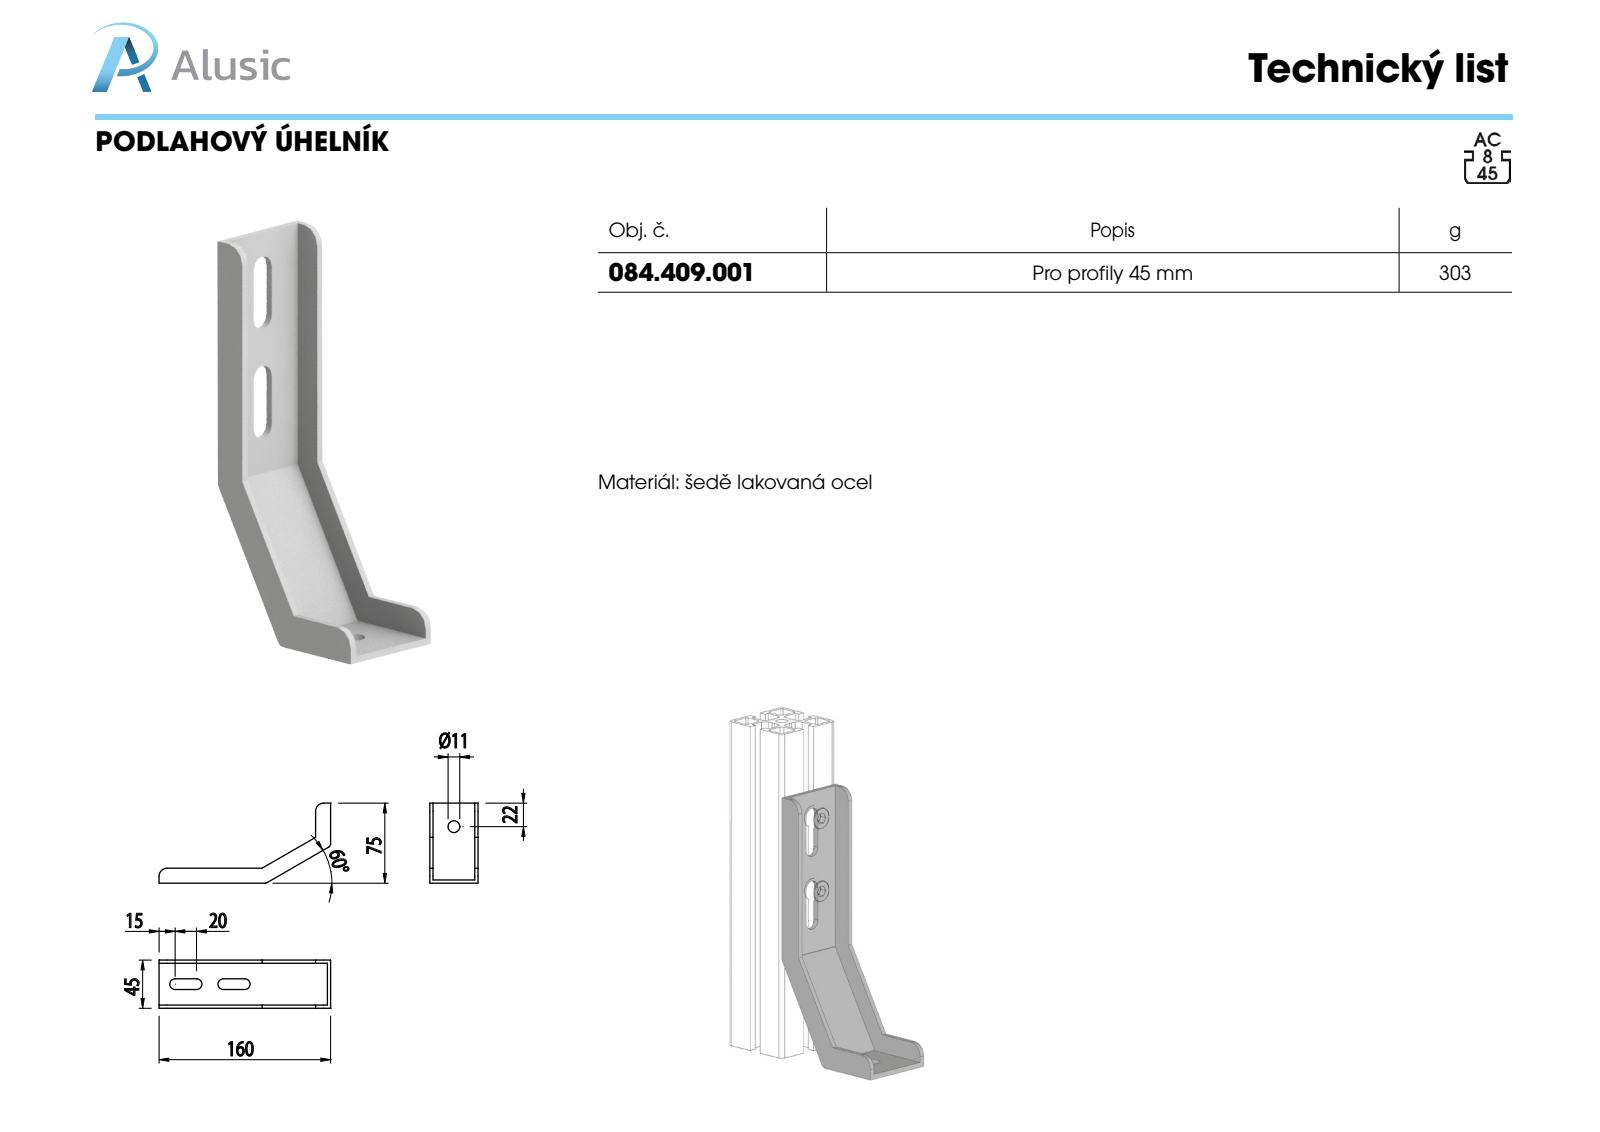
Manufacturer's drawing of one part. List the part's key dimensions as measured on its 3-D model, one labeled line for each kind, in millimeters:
Part name (STEP PRODUCT): 084.409.001
STEP written by: SolidWorks 2011 (CONFIG_CONTROL_DESIGN)
Units: millimetres
Bodies: 1 solid, 36 faces (22 planar, 14 cylindrical, 0 other)
Overall size (bounding box): 160.19 × 74.75 × 45
Volume: 38 681 mm³ · Surface area: 27 812 mm²
Round holes (diameter × count): ⌀11 ×1
Partial cylindrical surfaces — rounded edges, fillets, slot ends (radius × count): R5 ×4, R0.74 ×2, R3.74 ×2, R7.5 ×2
Main face-to-face distances: 3, 42, 45, 39, 14, 11, 17.5, 27.5, 14.5, 24.5
